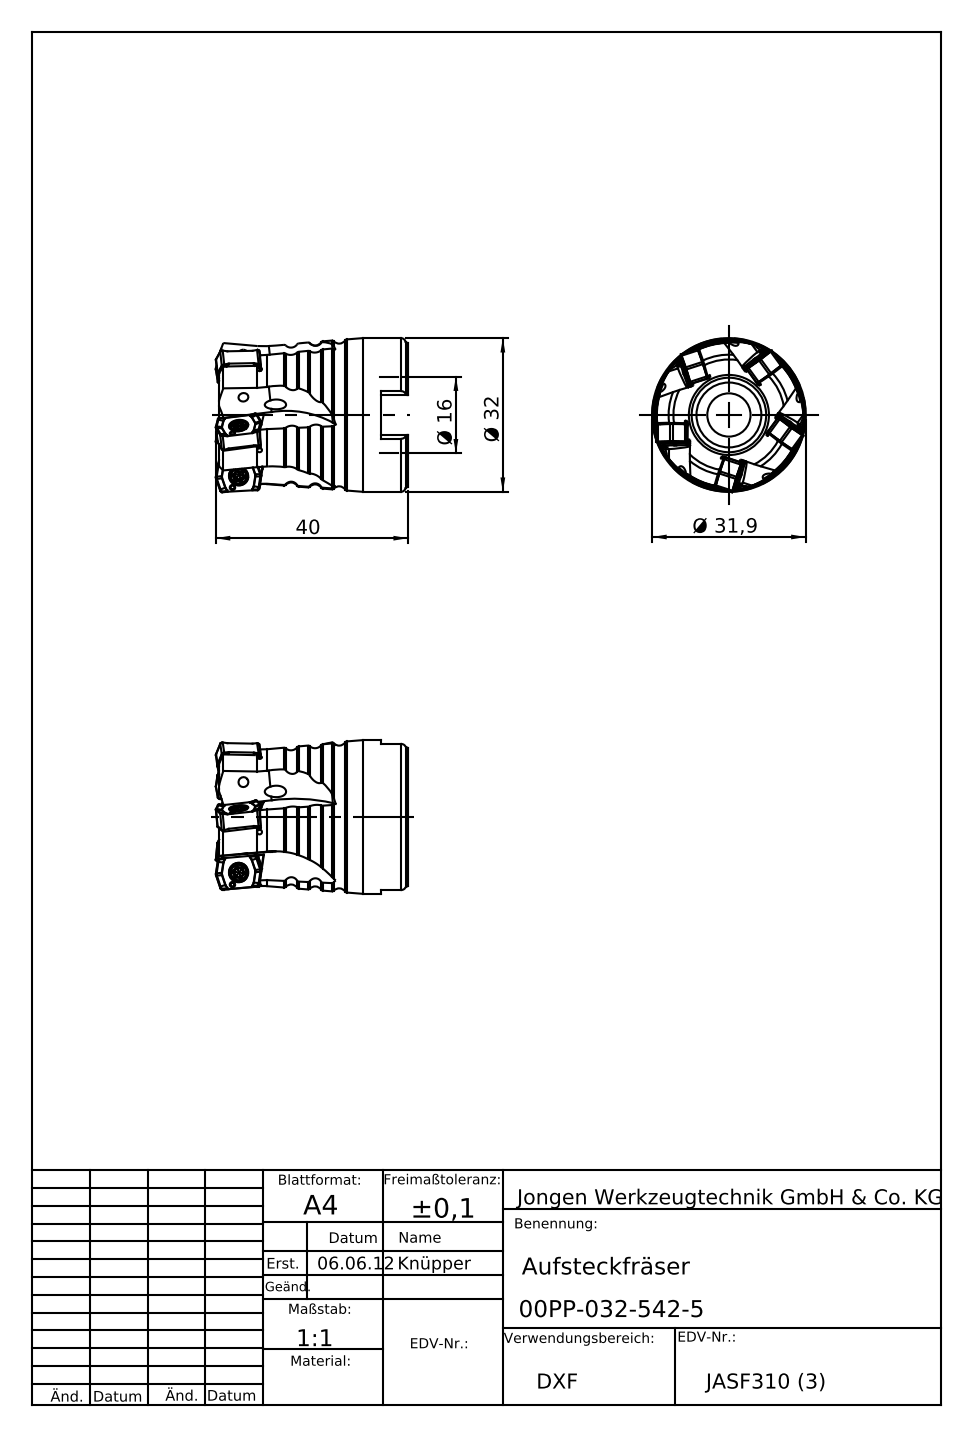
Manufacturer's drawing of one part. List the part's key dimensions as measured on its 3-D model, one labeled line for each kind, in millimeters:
Part name (STEP PRODUCT): 00PP-032-542-5
STEP written by: SolidWorks 2013 (AUTOMOTIVE_DESIGN)
Units: millimetres
Bodies: 1 solid, 187 faces (85 planar, 21 cylindrical, 81 other)
Overall size (bounding box): 38.32 × 32 × 32
Volume: 15 831 mm³ · Surface area: 7 028 mm²
Round holes (diameter × count): ⌀2.5 ×5, ⌀9 ×1, ⌀13.5 ×1, ⌀16 ×1, ⌀16.15 ×1, ⌀16.3 ×1
Round bosses / shafts (diameter × count): ⌀32 ×1
Partial cylindrical surfaces — rounded edges, fillets, slot ends (radius × count): R15 ×5, R14.4 ×1
Main face-to-face distances: 5.6, 26.8, 21.2, 8.4, 0.5, 19.95, 14.35, 6.85, 0.49, 37.8
